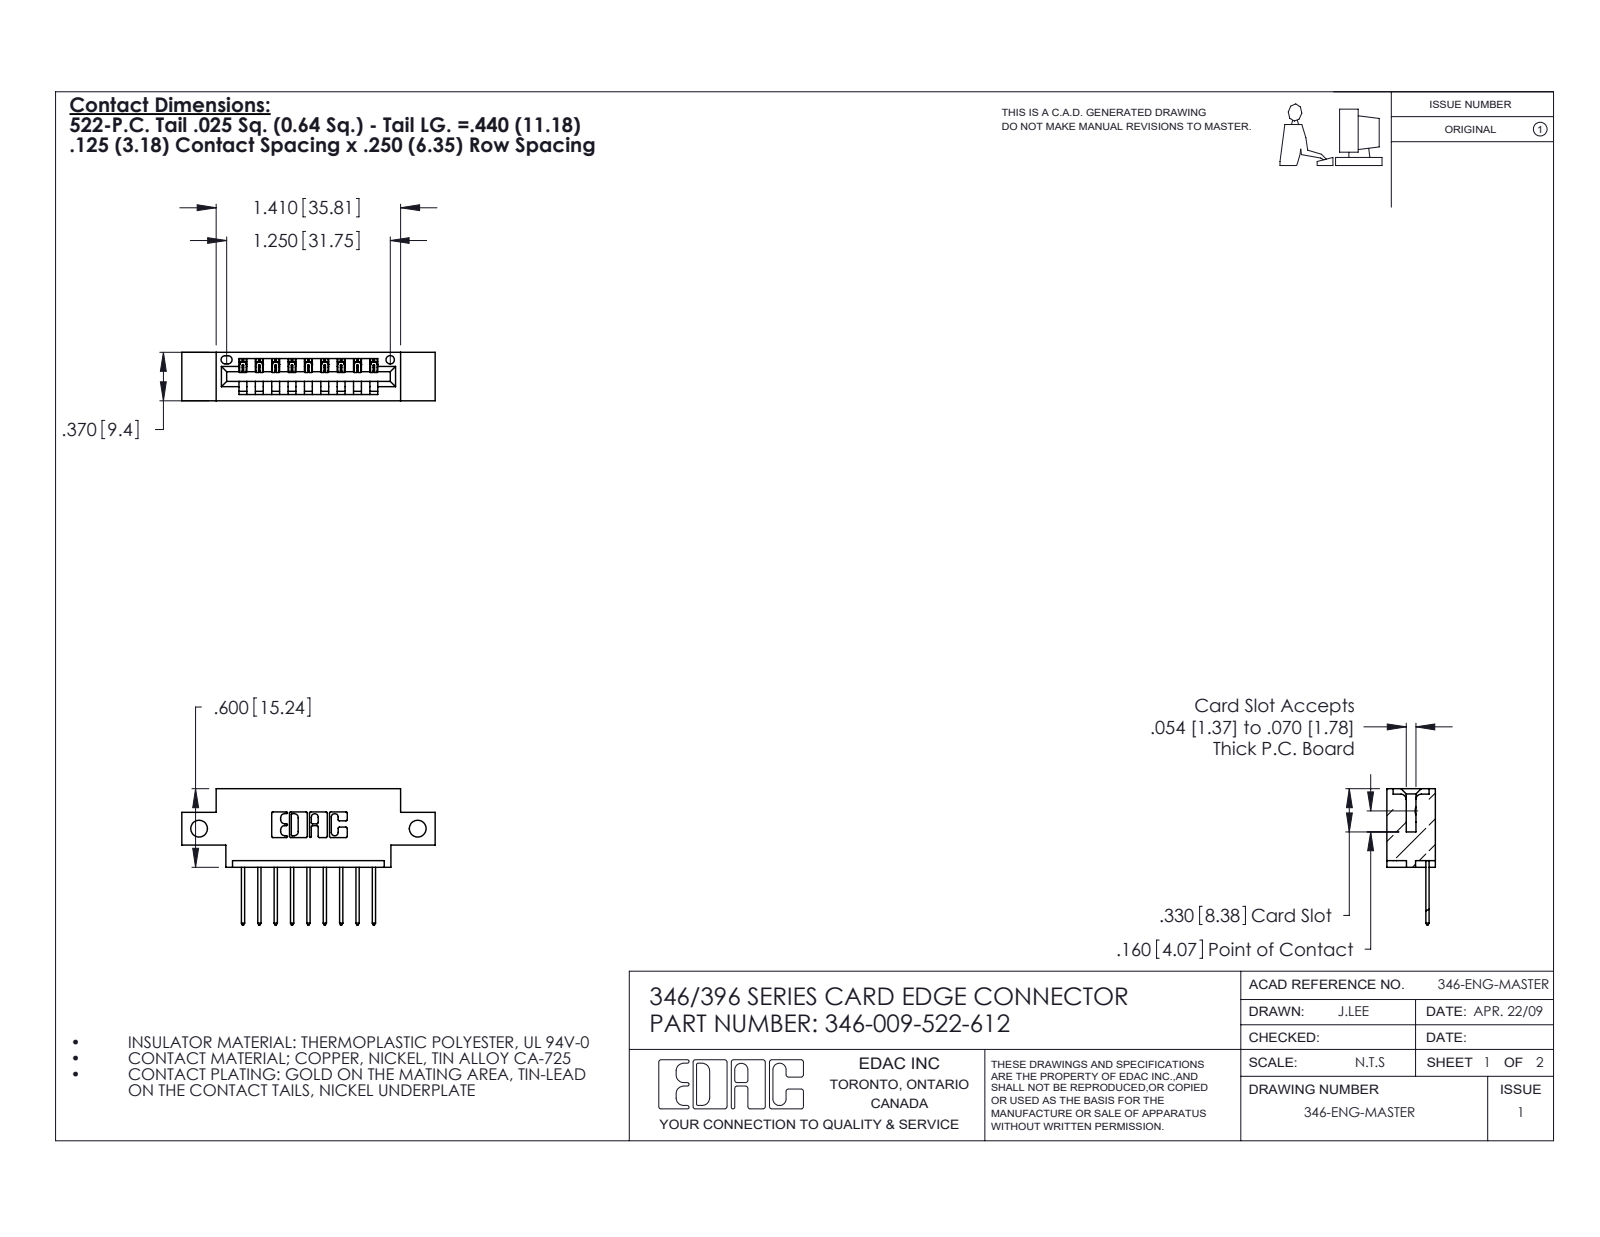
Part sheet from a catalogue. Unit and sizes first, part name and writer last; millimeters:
Units: millimetres
Overall size (bounding box): 49.1 × 26.4 × 9.4
Round holes (diameter × count): ⌀3.3 ×2, ⌀1.6 ×1
Partial cylindrical surfaces — rounded edges, fillets, slot ends (radius × count): R0.3 ×22, R0.2 ×18, R0.3 ×18, R0.2 ×6, R0.8 ×6, R0.7 ×3, R0.8 ×2, R1 ×2
Main face-to-face distances: 6.4, 9.4, 1.2, 8.2, 1.8, 7.6, 0.6, 3.8, 5.6, 2.5
Hole centre spacings: 42.4
Volume: 4 240 mm³ · Surface area: 4 986 mm²
Bodies: 10 solids, 648 faces (440 planar, 208 cylindrical, 0 other)
Part name (STEP PRODUCT): 346 Part_0.170 Offset - Side Mount; 346-009-522-612; 345-292-001_345-293-122
STEP written by: SolidWorks 2020 (CONFIG_CONTROL_DESIGN)
